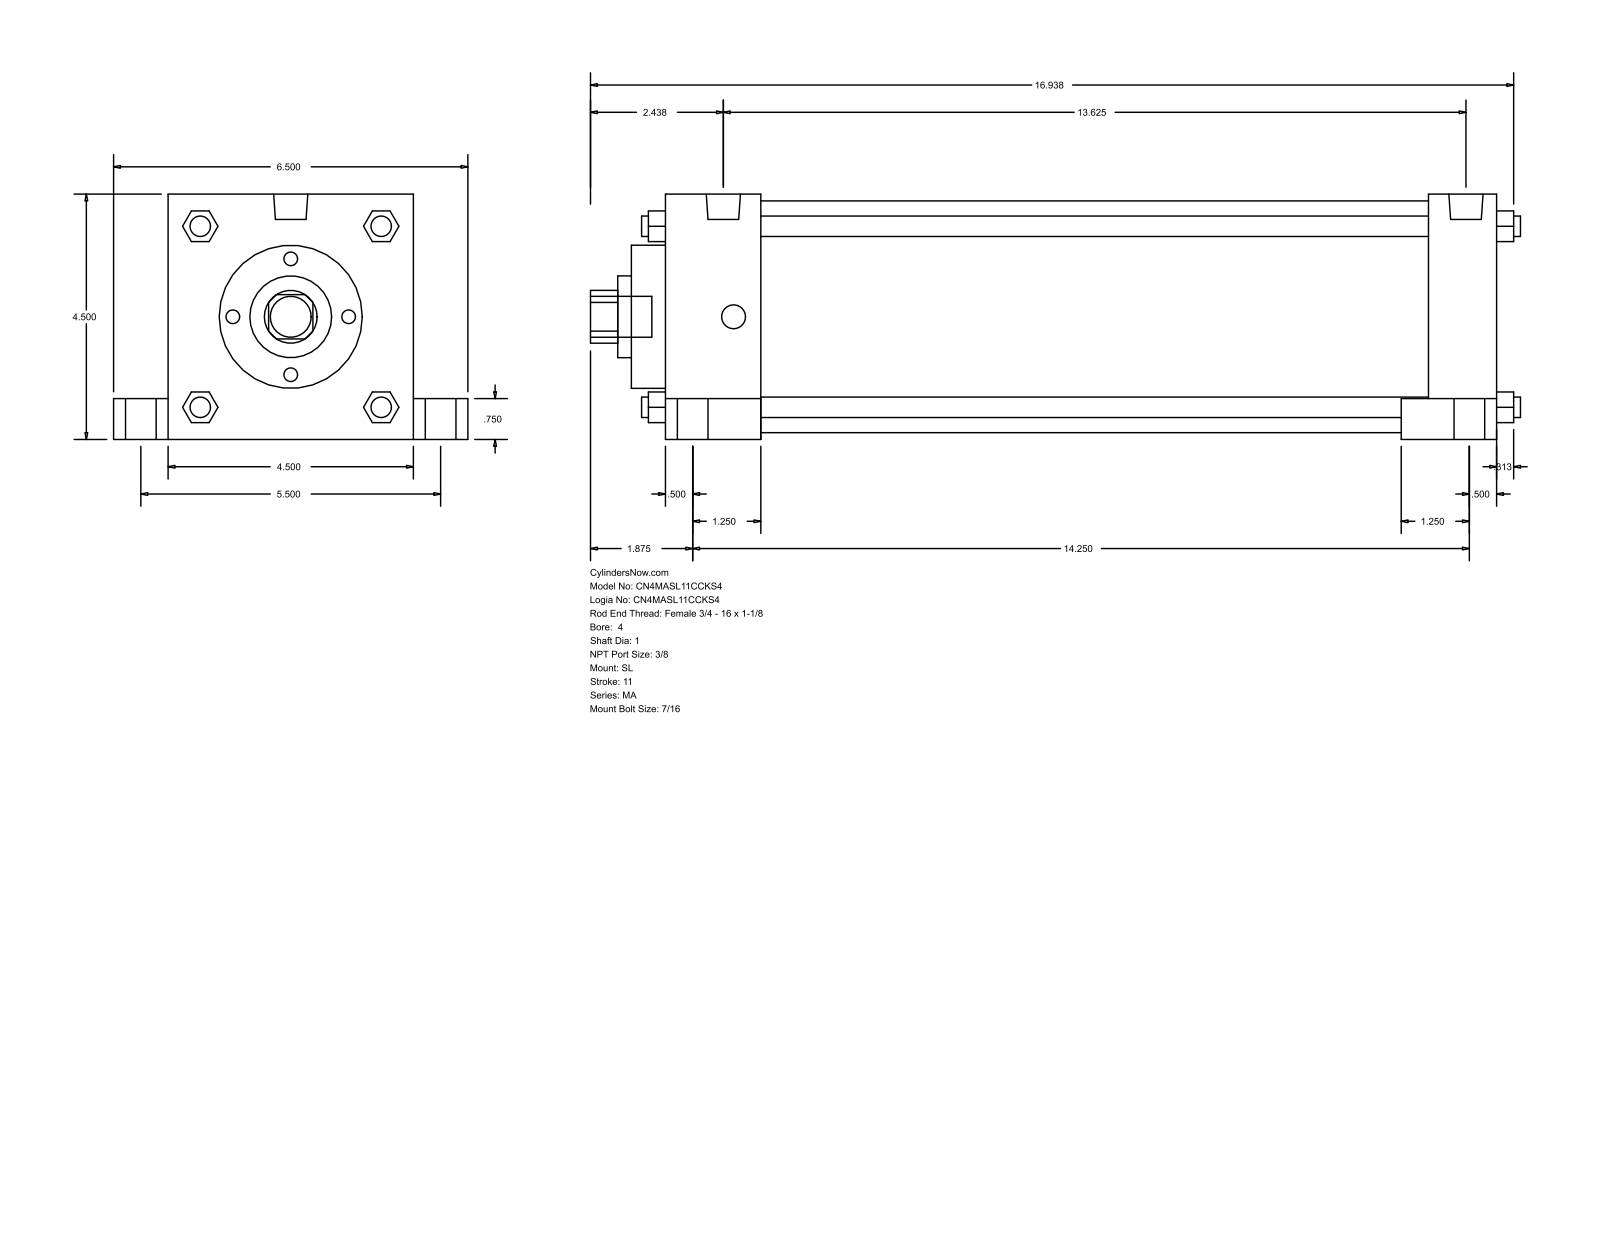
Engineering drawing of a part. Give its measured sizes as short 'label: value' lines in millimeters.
name: MA_SL__0400_1
written by: GSSL Pune (CONFIG_CONTROL_DESIGN)
unit: mm
bodies: 0 solids, 150 faces (113 planar, 37 cylindrical, 0 other)
size: 433.39 × 165.1 × 114.3
holes: 1× ⌀25.4, 1× ⌀38.1, 1× ⌀66.67, 1× ⌀107.95
bosses: 4× ⌀20.64, 4× ⌀14.29, 4× ⌀11.11, 4× ⌀9.53, 2× ⌀15.93, 1× ⌀19.05
rounds: 1× R12.29
face distances: 114.3, 387.35, 44.46, 342.89, 355.6, 311.14, 31.75, 25.4, 139.7, 403.22
